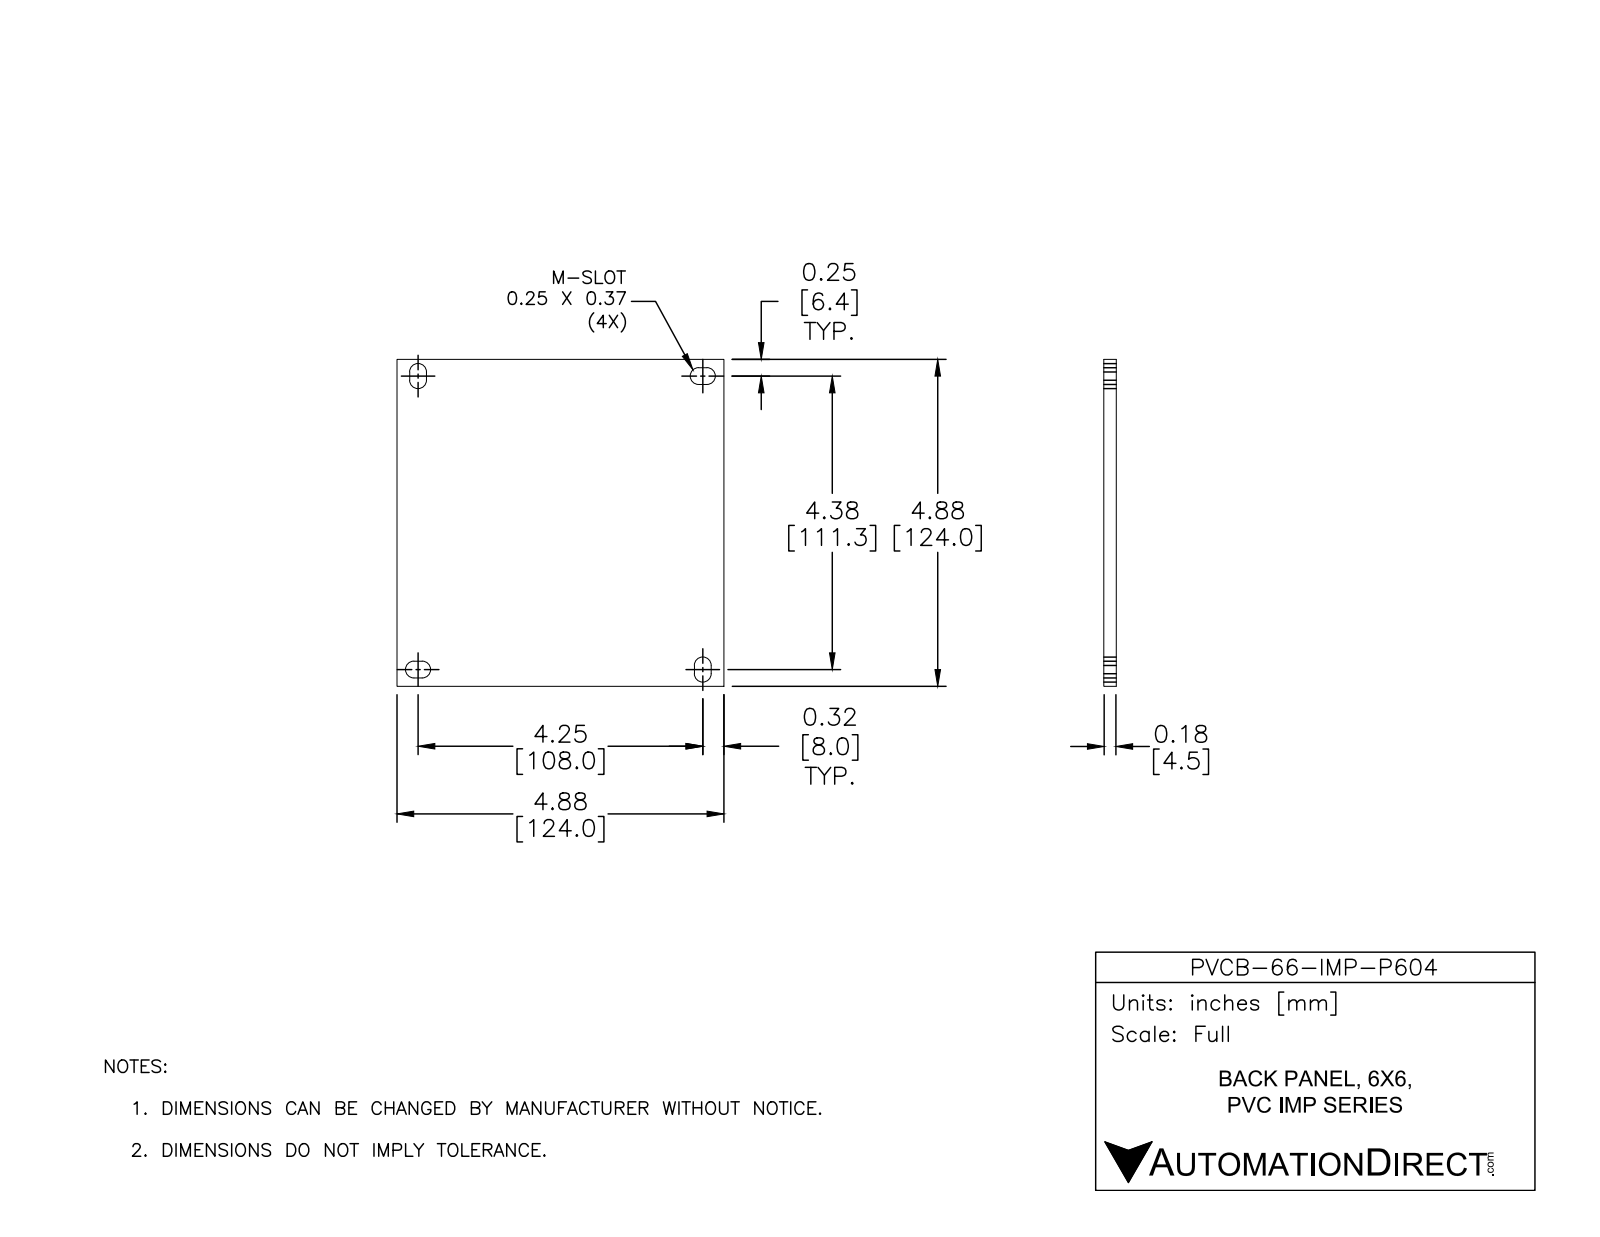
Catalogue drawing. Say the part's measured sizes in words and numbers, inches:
The part is named "PVCBP-66-IMP-P604". Its 3-D file was written by "SolidWorks 2016 (AUTOMOTIVE_DESIGN)". It is 1 solid with 24 faces: 14 planar, 10 cylindrical and 0 other. Overall it measures 4.88 by 4.88 by 0.064 inches. Its volume is 1.506 cubic inches and its surface area 48.51 square inches. Partial cylindrical surfaces (rounded edges, fillets, slot ends): 8 of radius 0.125. The main face-to-face distances are 0.064, 4.88, 0.25, 0.125, 0.375, 4.505, 4.755, 4.38, 4.25, 4.63.
